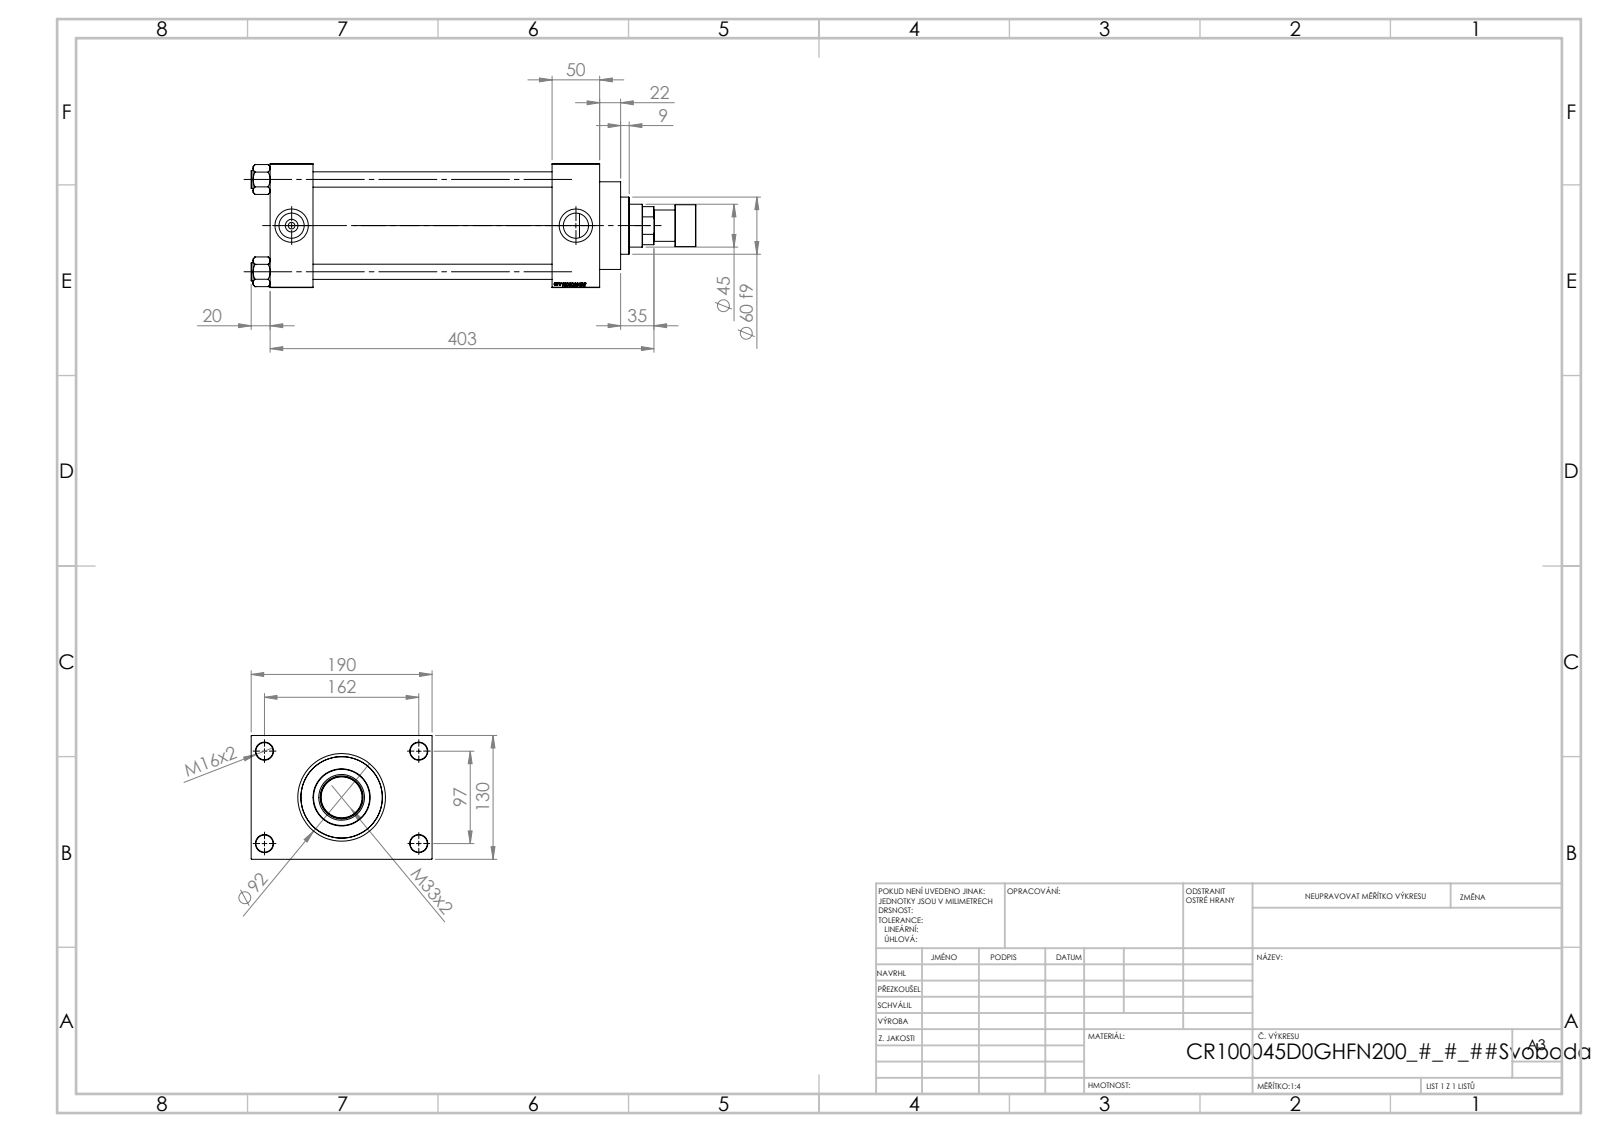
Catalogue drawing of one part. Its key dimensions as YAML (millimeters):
part_name: "V215_VC_A; V215CR_D_Body; NUT_M5_D; V215CR_VCP_D (+2 more)"
step_written_by: "SolidWorks 2019 (CONFIG_CONTROL_DESIGN)"
units: millimeters
bodies: {solids: 12, faces: 1164, planar: 548, cylindrical: 92, other: 524}
overall_size: [467, 190, 130]
volume: 3249000
surface_area: 541384
round_holes:
  - {diameter: 16, count: 4}
  - {diameter: 18, count: 4}
  - {diameter: 7, count: 2}
  - {diameter: 26.44, count: 2}
  - {diameter: 35, count: 2}
  - {diameter: 31.5, count: 1}
  - {diameter: 45, count: 1}
  - {diameter: 48, count: 1}
  - {diameter: 76, count: 1}
  - {diameter: 85.5, count: 1}
  - {diameter: 100, count: 1}
round_bosses_or_shafts:
  - {diameter: 19, count: 4}
  - {diameter: 106, count: 1}
  - {diameter: 92, count: 1}
  - {diameter: 60, count: 1}
  - {diameter: 44, count: 1}
  - {diameter: 33, count: 1}
face_to_face_distances: [130, 45, 296, 251, 346, 301, 50, 30, 160, 96]
hole_center_spacings: [32.55, 68.52, 94.41, 96.9, 102.27, 129.45, 161.73, 97]
